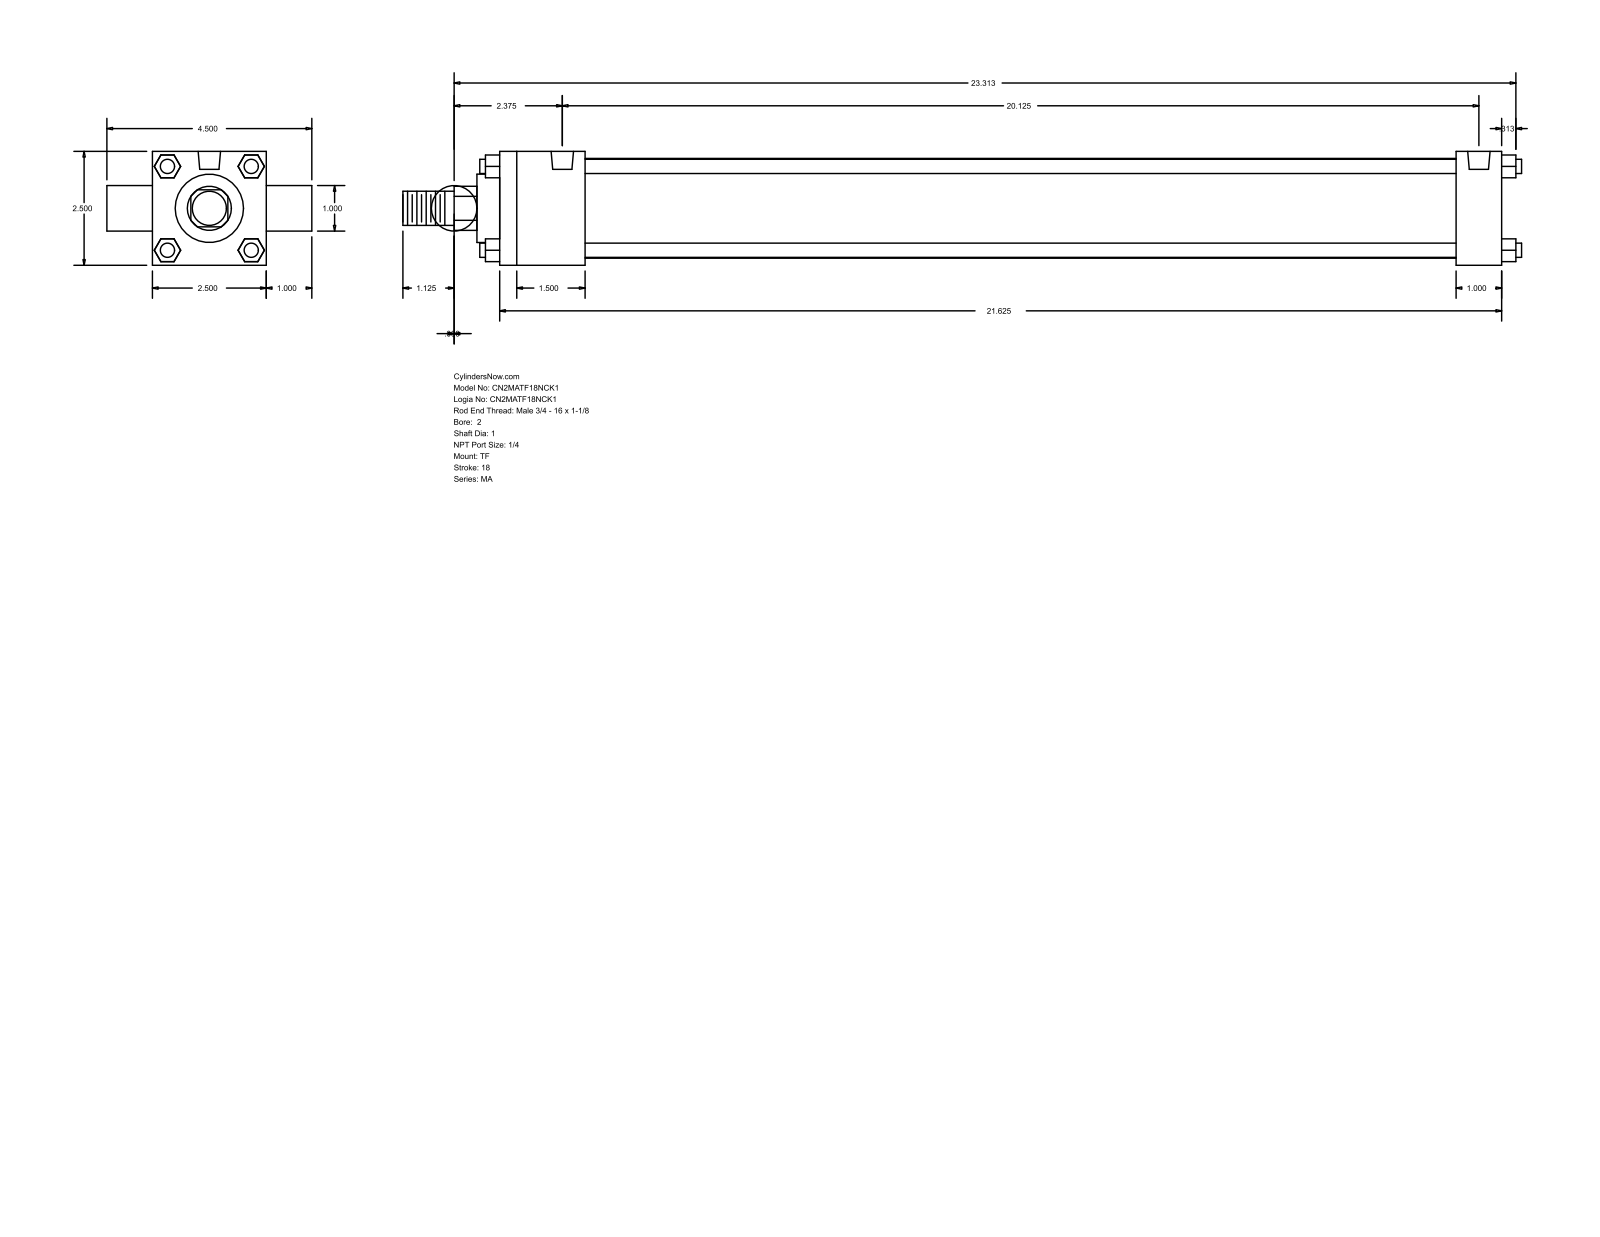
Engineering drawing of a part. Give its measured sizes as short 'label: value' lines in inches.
name: MA_TF__0200_1
written by: GSSL Pune (CONFIG_CONTROL_DESIGN)
unit: in
bodies: 0 solids, 120 faces (92 planar, 28 cylindrical, 0 other)
size: 24.563 × 4.5 × 2.5
holes: 3× ⌀0.313, 2× ⌀0.492
bosses: 4× ⌀0.313, 2× ⌀1, 1× ⌀2.19, 1× ⌀1.5, 1× ⌀0.75
rounds: 1× R0.484
face distances: 2.5, 1, 22, 0.5, 1.875, 21, 19.125, 20.125, 3.5, 0.92
hole spacings: 20.125
